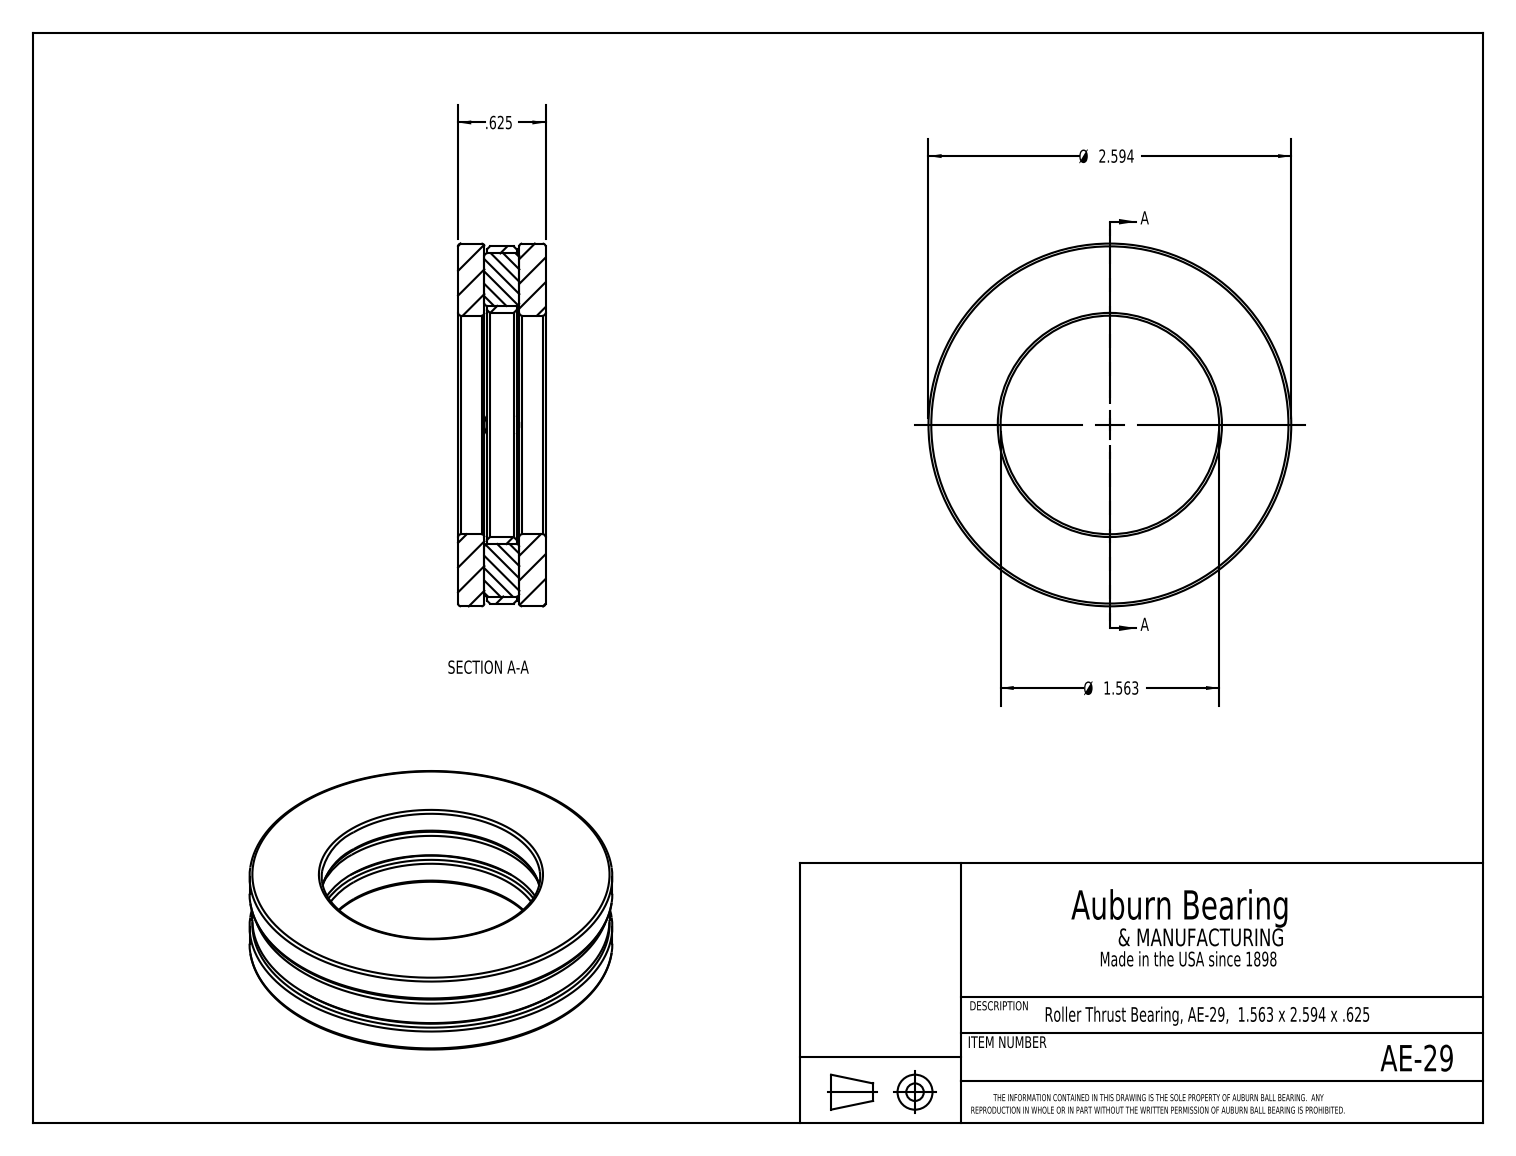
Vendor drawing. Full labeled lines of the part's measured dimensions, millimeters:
Part name (STEP PRODUCT): AE-29
STEP written by: SolidWorks 2017 (CONFIG_CONTROL_DESIGN)
Units: millimetres
Bodies: 7 solids, 60 faces (30 planar, 10 cylindrical, 20 other)
Overall size (bounding box): 65.9 × 65.9 × 15.9
Volume: 31 120 mm³ · Surface area: 18 310 mm²
Round holes (diameter × count): ⌀39.7 ×1, ⌀40.7 ×1
Round bosses / shafts (diameter × count): ⌀6.4 ×2, ⌀65.9 ×1, ⌀64.9 ×1
Main face-to-face distances: 5.3, 10.6, 6.4, 4.7, 11.1, 15.9, 11.1, 4.8, 5.8, 0.5
